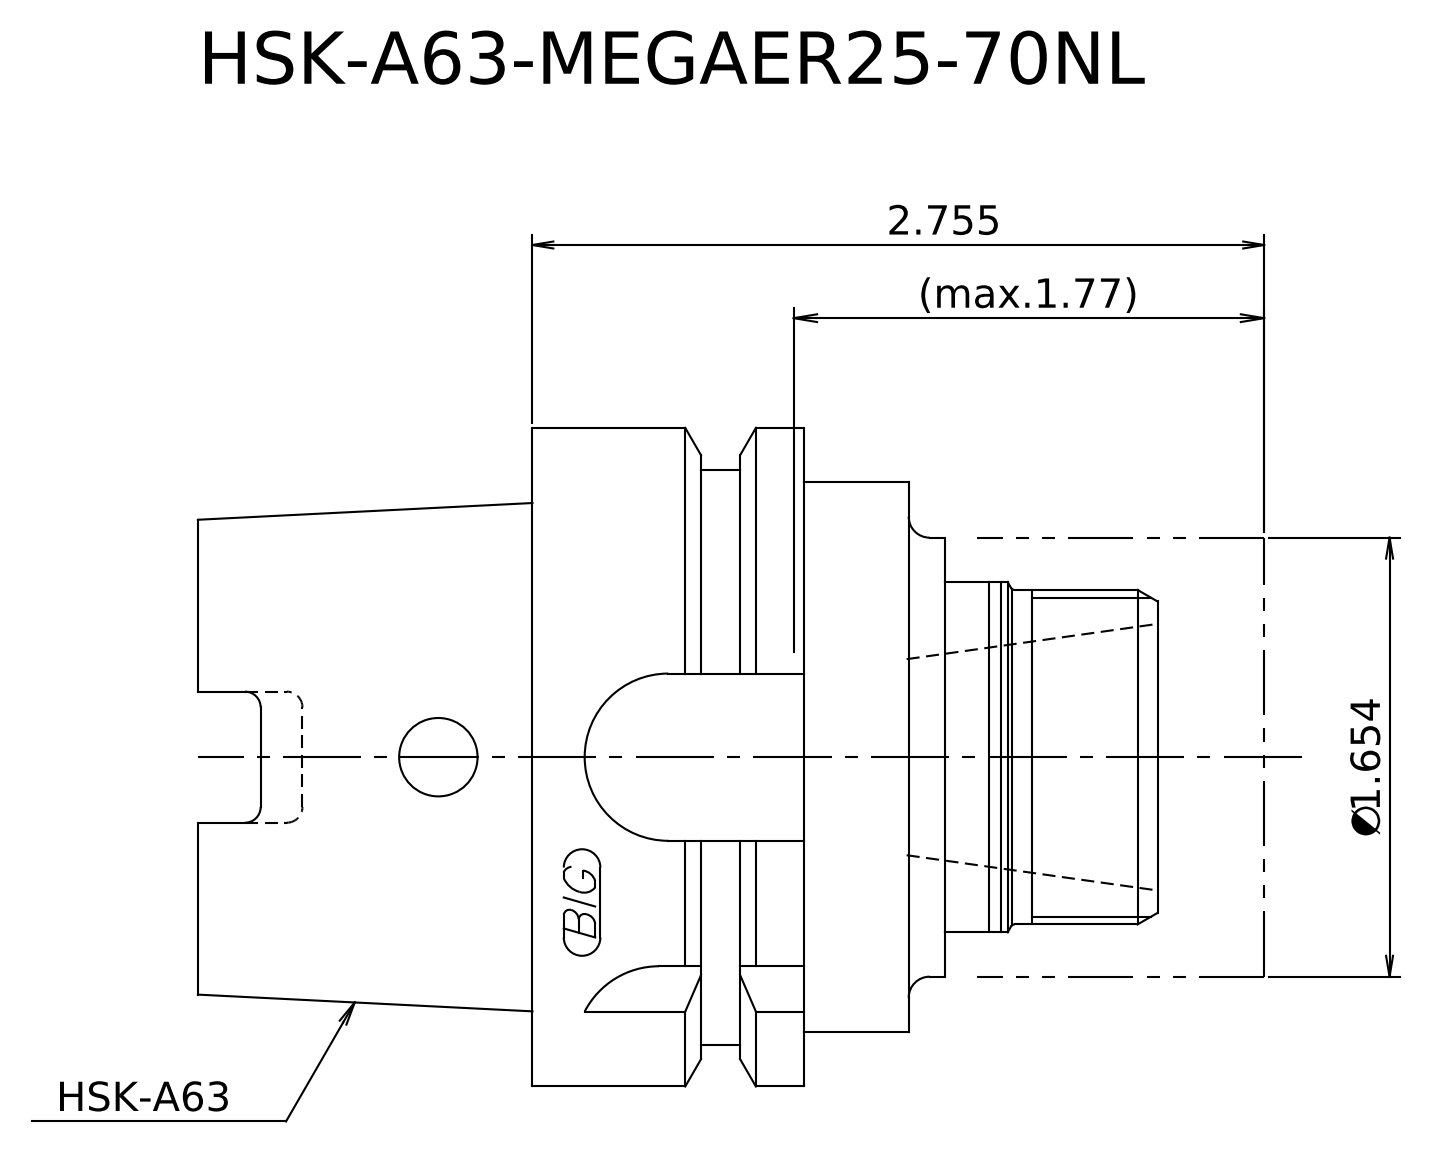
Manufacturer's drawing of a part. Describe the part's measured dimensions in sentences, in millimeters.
Its 3-D file was written by "Kubotek KeyCreator 2011 V10.0.2 (22737) (automotive_design)". It is 2 solids with 24 faces: 10 planar, 8 cylindrical and 6 other. Overall it measures 102 by 63 by 63 millimeters. Its volume is 214 786 cubic millimeters and its surface area 27 132 square millimeters. Round bosses or shafts: 1 of diameter 63, 1 of diameter 55, 1 of diameter 52.6, 1 of diameter 42, 1 of diameter 33.5, 1 of diameter 32. The main face-to-face distances are 74.5, 27.5, 102, 70, 42.5, 32, 44, 16.5, 26, 58.
